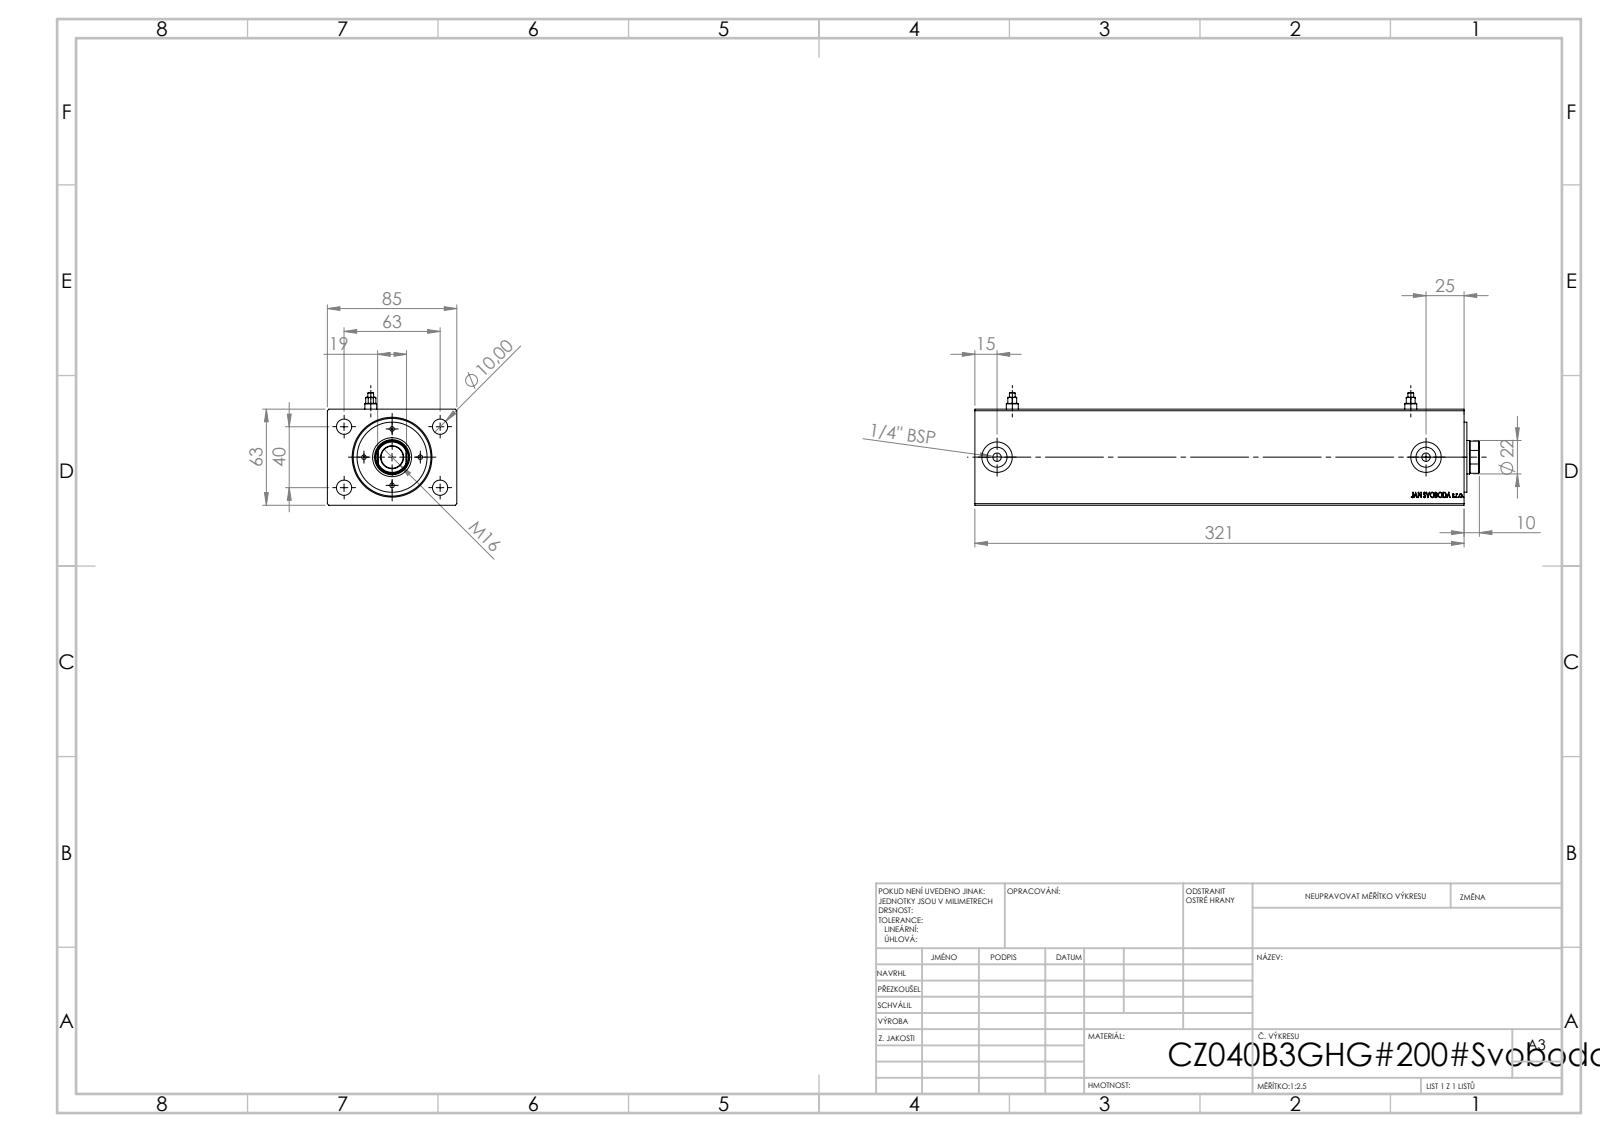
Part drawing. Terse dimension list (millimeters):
name: V500CZ; Zatka_Cushioning3; V500CZ_B_VC
written by: SolidWorks 2019 (CONFIG_CONTROL_DESIGN)
unit: mm
bodies: 4 solids, 934 faces (424 planar, 74 cylindrical, 436 other)
size: 331 × 85 × 74
volume: 214 711 mm³; area: 188 488 mm²
holes: 4× ⌀3, 4× ⌀10, 2× ⌀1.8, 2× ⌀5.5, 2× ⌀8, 2× ⌀13.16, 2× ⌀20, 1× ⌀14.5, 1× ⌀22, 1× ⌀23, 1× ⌀36, 1× ⌀40
bosses: 2× ⌀7.8, 2× ⌀3.8, 1× ⌀46
rounds: 1× R10.5
face distances: 63, 85, 321, 305.7, 15.3, 10, 1.8, 8.2, 297.5, 312.8
hole spacings: 18.5, 23.85, 26.16, 31.54, 37.31, 49.74, 53.85, 37
